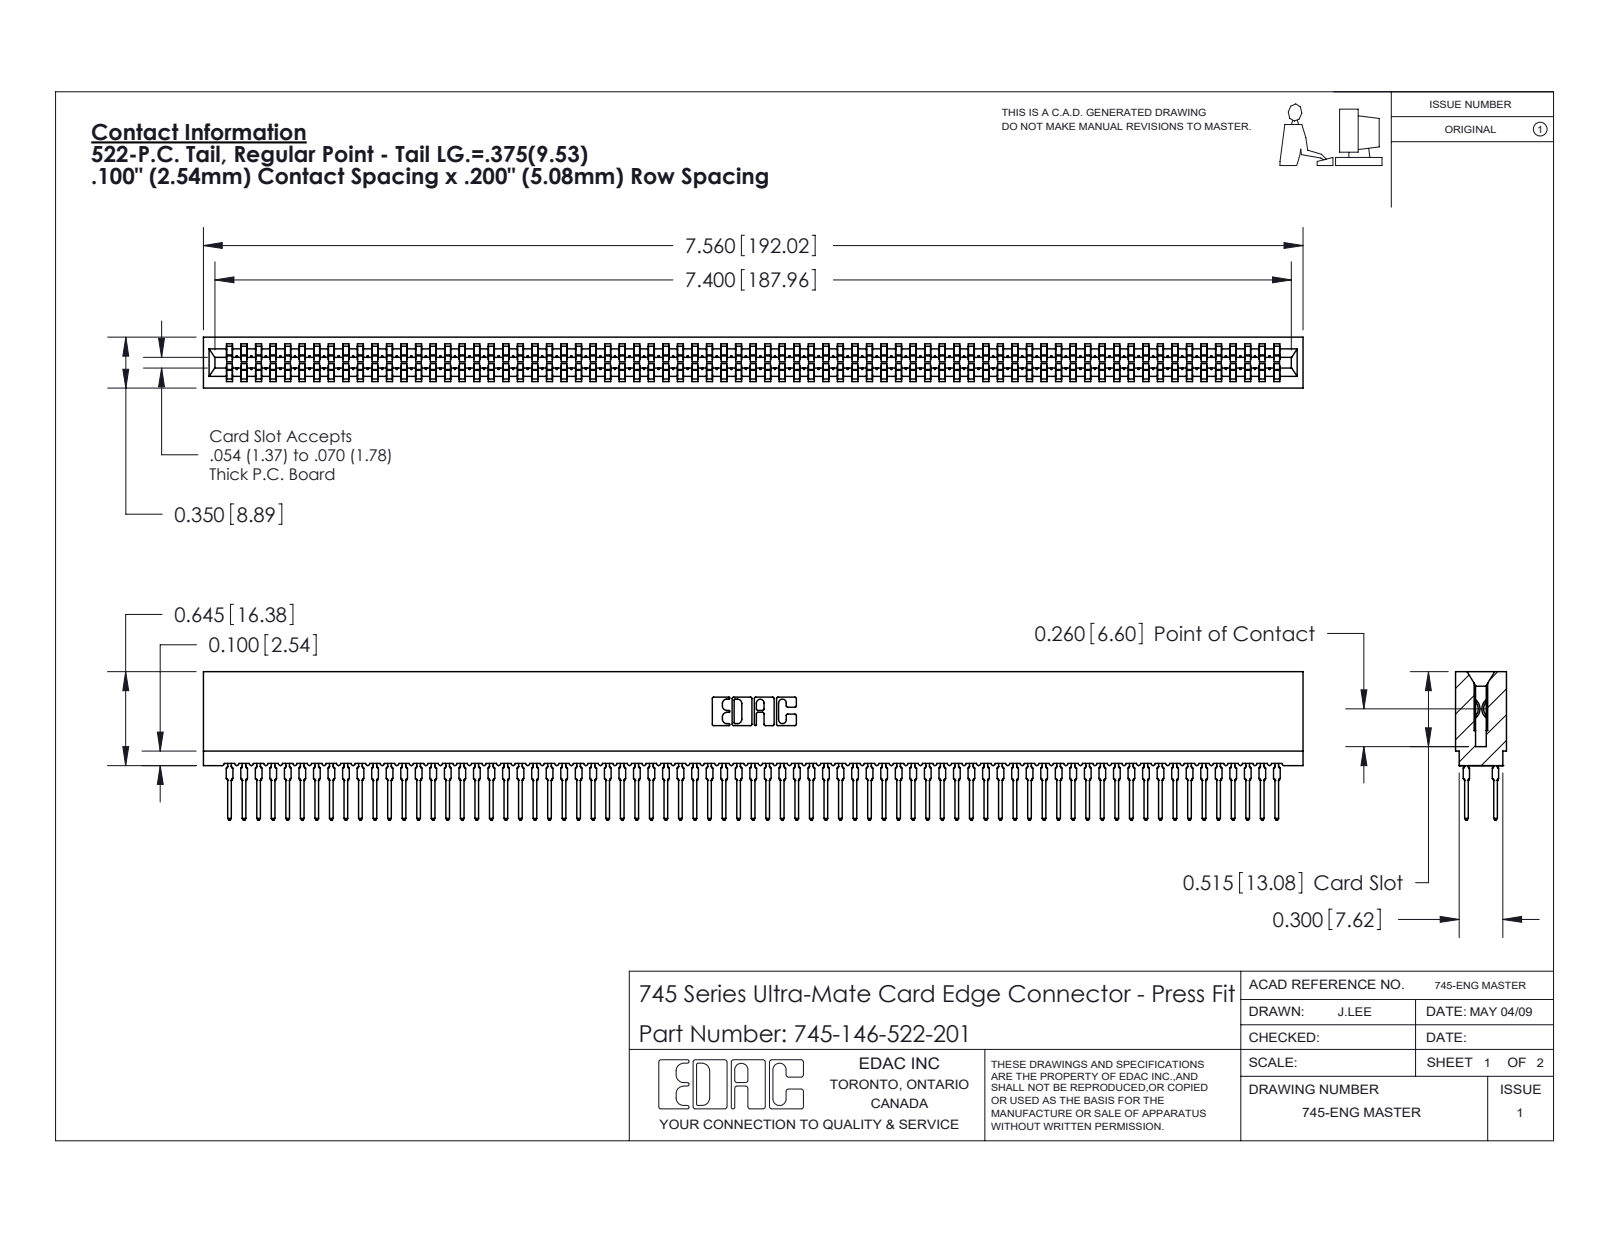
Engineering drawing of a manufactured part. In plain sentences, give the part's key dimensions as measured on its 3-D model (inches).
The part is named "745-146-522-201; 745 Part_Insulator Option - 01; 745-292-001_522". Its 3-D file was written by "SolidWorks 2020 (CONFIG_CONTROL_DESIGN)". It is 147 solids with 13162 faces: 6771 planar, 2595 cylindrical and 3796 other. Overall it measures 7.56 by 1.021 by 0.35 inches. Its volume is 1.053 cubic inches and its surface area 56.28 square inches. Partial cylindrical surfaces (rounded edges, fillets, slot ends): 292 of radius 0.021, 146 of radius 0.015, 22 of radius 0.01, 8 of radius 0.005, 8 of radius 0.011, 6 of radius 0.007, 6 of radius 0.031, 3 of radius 0.026. The main face-to-face distances are 0.35, 0.063, 0.287, 0.045, 0.305, 0.018, 0.243, 0.138, 0.212, 0.093.
